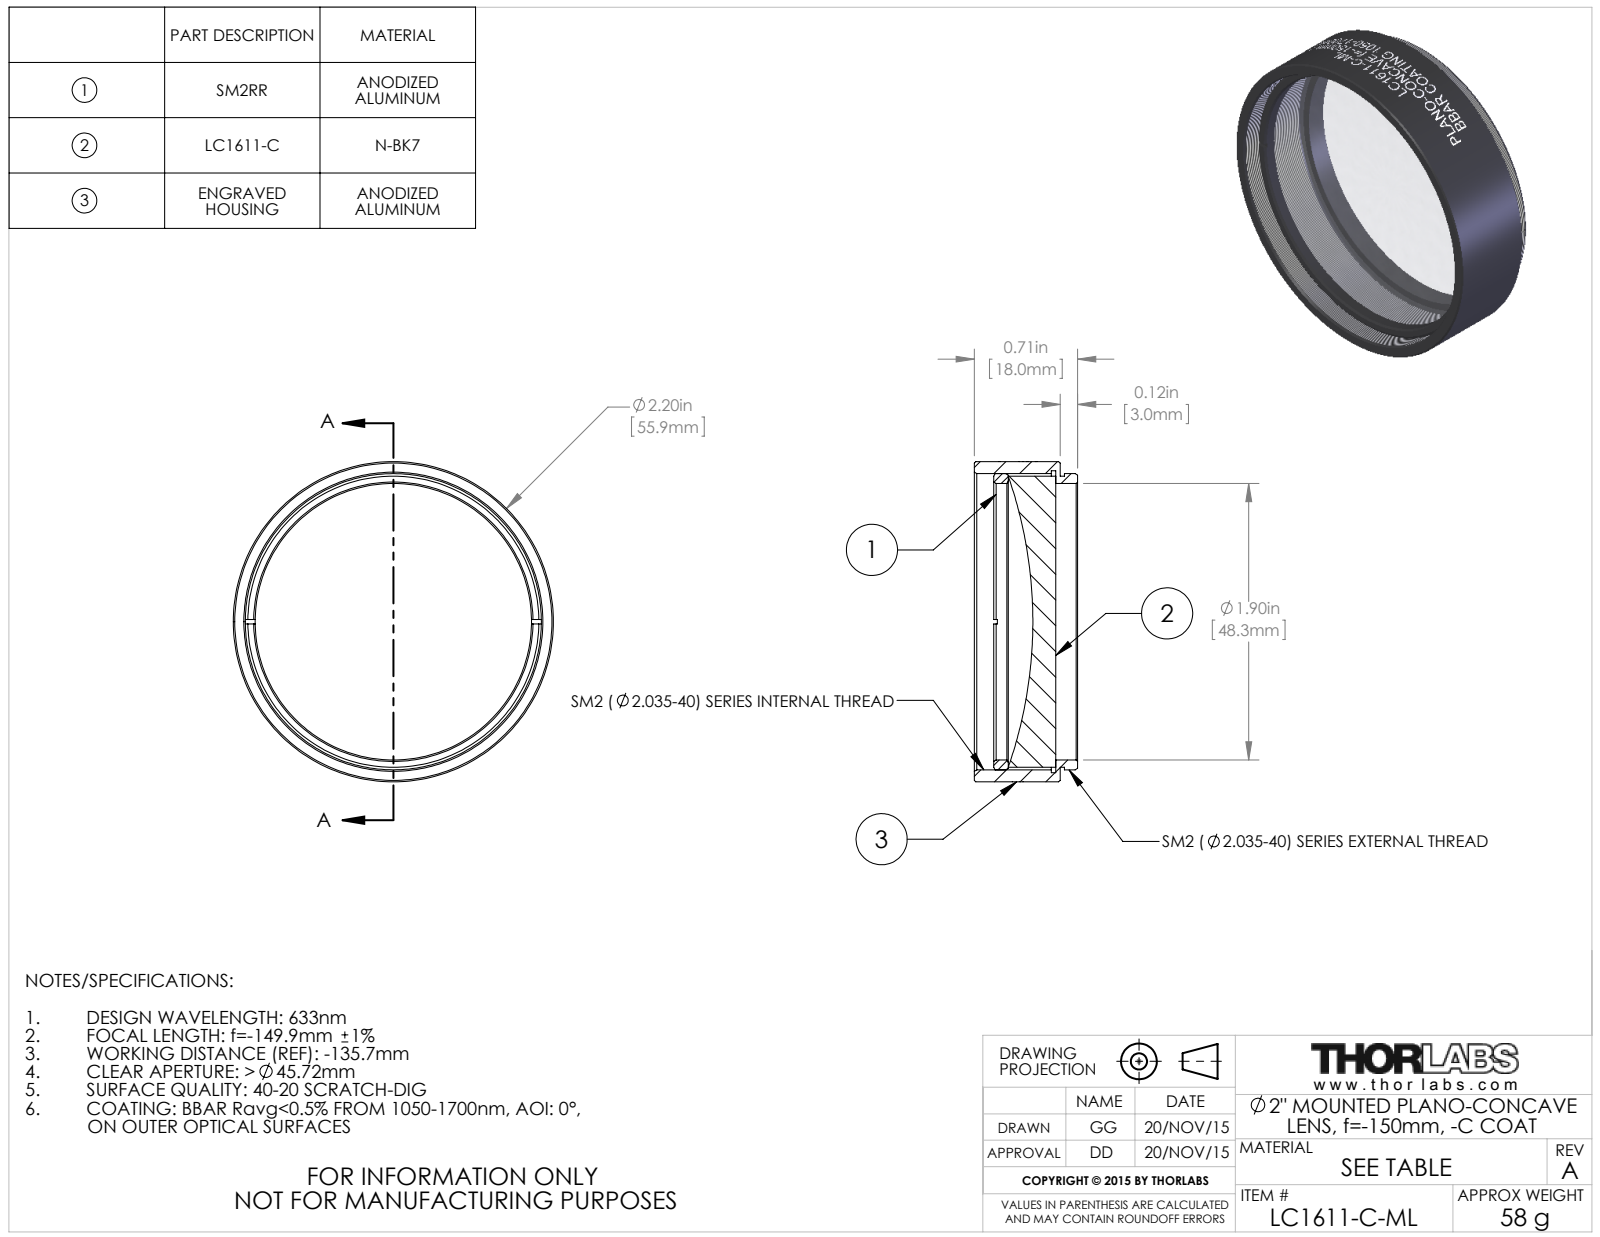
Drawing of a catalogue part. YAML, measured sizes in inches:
part_name: "TTN045374-E0W"
step_written_by: "SolidWorks 2014 (CONFIG_CONTROL_DESIGN)"
units: inches
bodies: {solids: 3, faces: 147, planar: 16, cylindrical: 109, other: 22}
overall_size: [2.2, 2.2, 0.71]
volume: 1.175
surface_area: 21.85
round_holes:
  - {diameter: 1.9, count: 1}
  - {diameter: 2.075, count: 1}
round_bosses_or_shafts:
  - {diameter: 2.2, count: 1}
  - {diameter: 2.035, count: 1}
  - {diameter: 2, count: 1}
  - {diameter: 1.999, count: 1}
face_to_face_distances: [0.03, 0.59, 0.56, 0.12, 0.15, 0.71, 0.477, 0.357, 0.327, 0.233]
